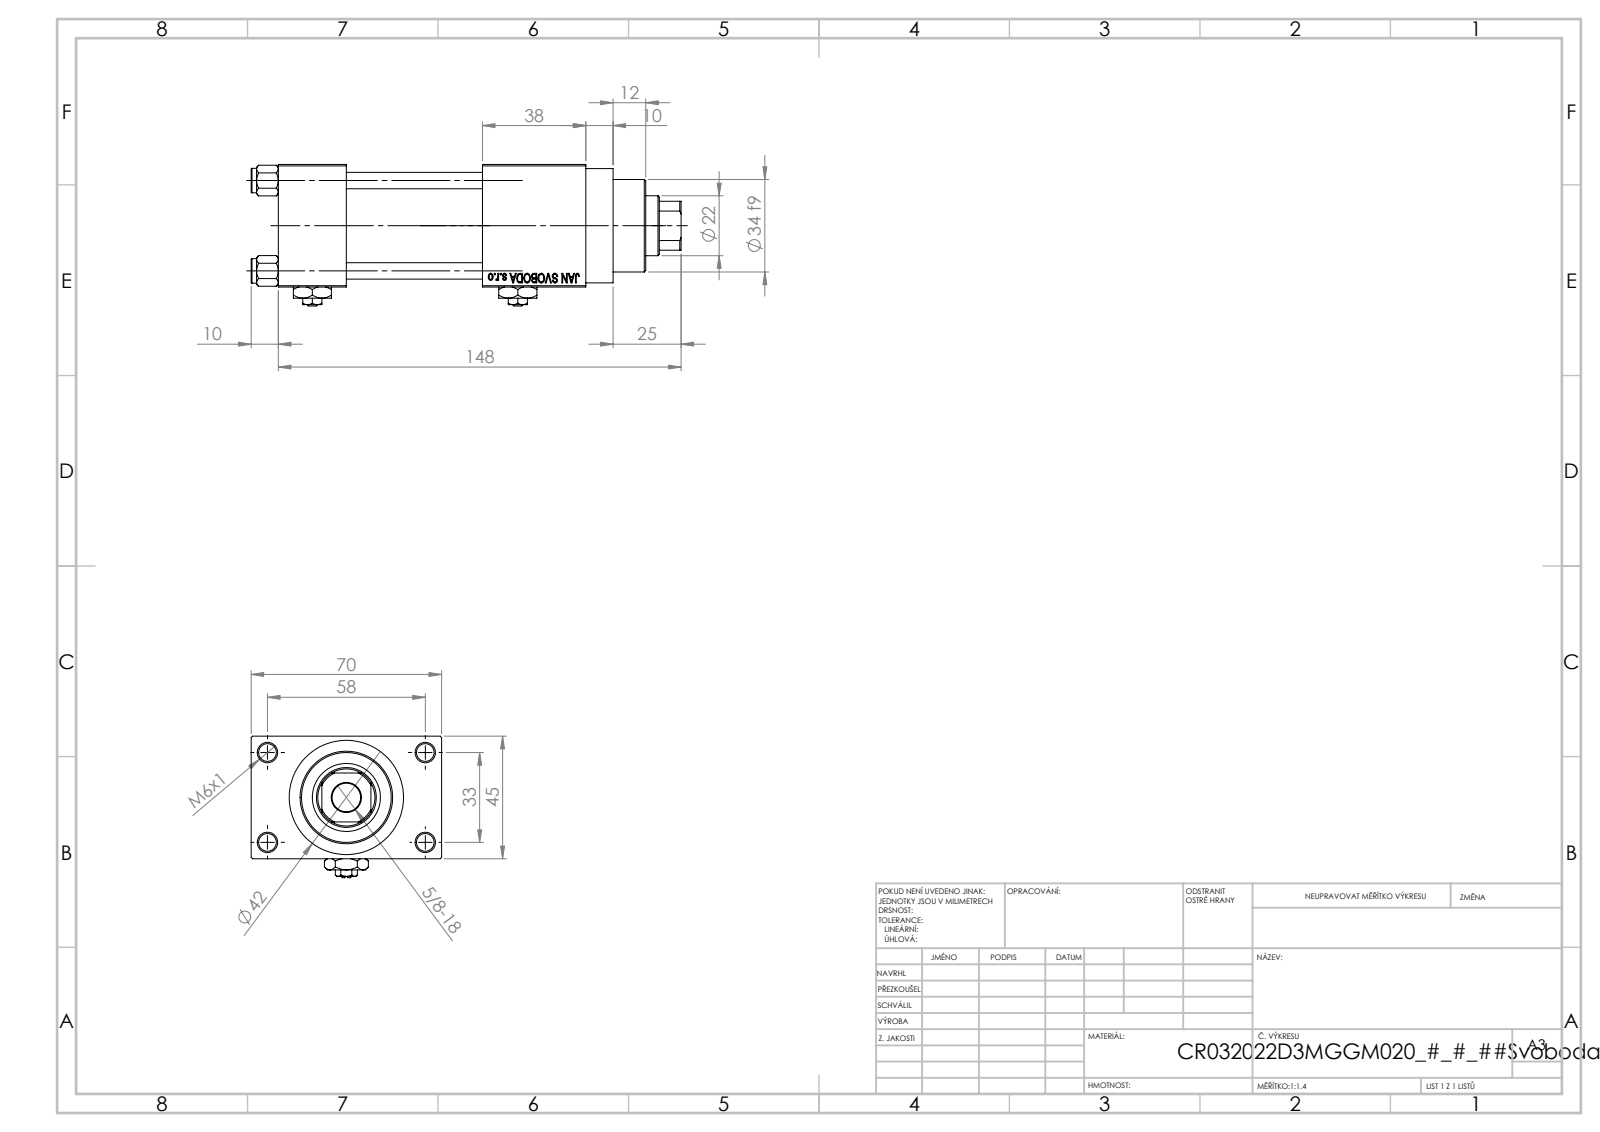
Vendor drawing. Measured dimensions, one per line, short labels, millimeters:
name: NUT_M5_D; V215_VC_A; Zatka_pro_OIL_PORT; V215CR_D_Body (+2 more)
written by: SolidWorks 2019 (CONFIG_CONTROL_DESIGN)
unit: mm
bodies: 13 solids, 1202 faces (542 planar, 100 cylindrical, 560 other)
size: 158 × 70 × 52
volume: 243 368 mm³; area: 81 200 mm²
holes: 4× ⌀6, 4× ⌀6.5, 2× ⌀7, 2× ⌀13.16, 2× ⌀20, 1× ⌀10.5, 1× ⌀22, 1× ⌀24, 1× ⌀25, 1× ⌀32, 1× ⌀33
bosses: 4× ⌀9, 1× ⌀42, 1× ⌀38, 1× ⌀34
rounds: 1× R10.5
face distances: 45, 25, 12.5, 57.5, 50, 75, 88, 70, 38, 113
hole spacings: 12.4, 23.48, 33.2, 33.37, 35.35, 45.6, 56.35, 33
